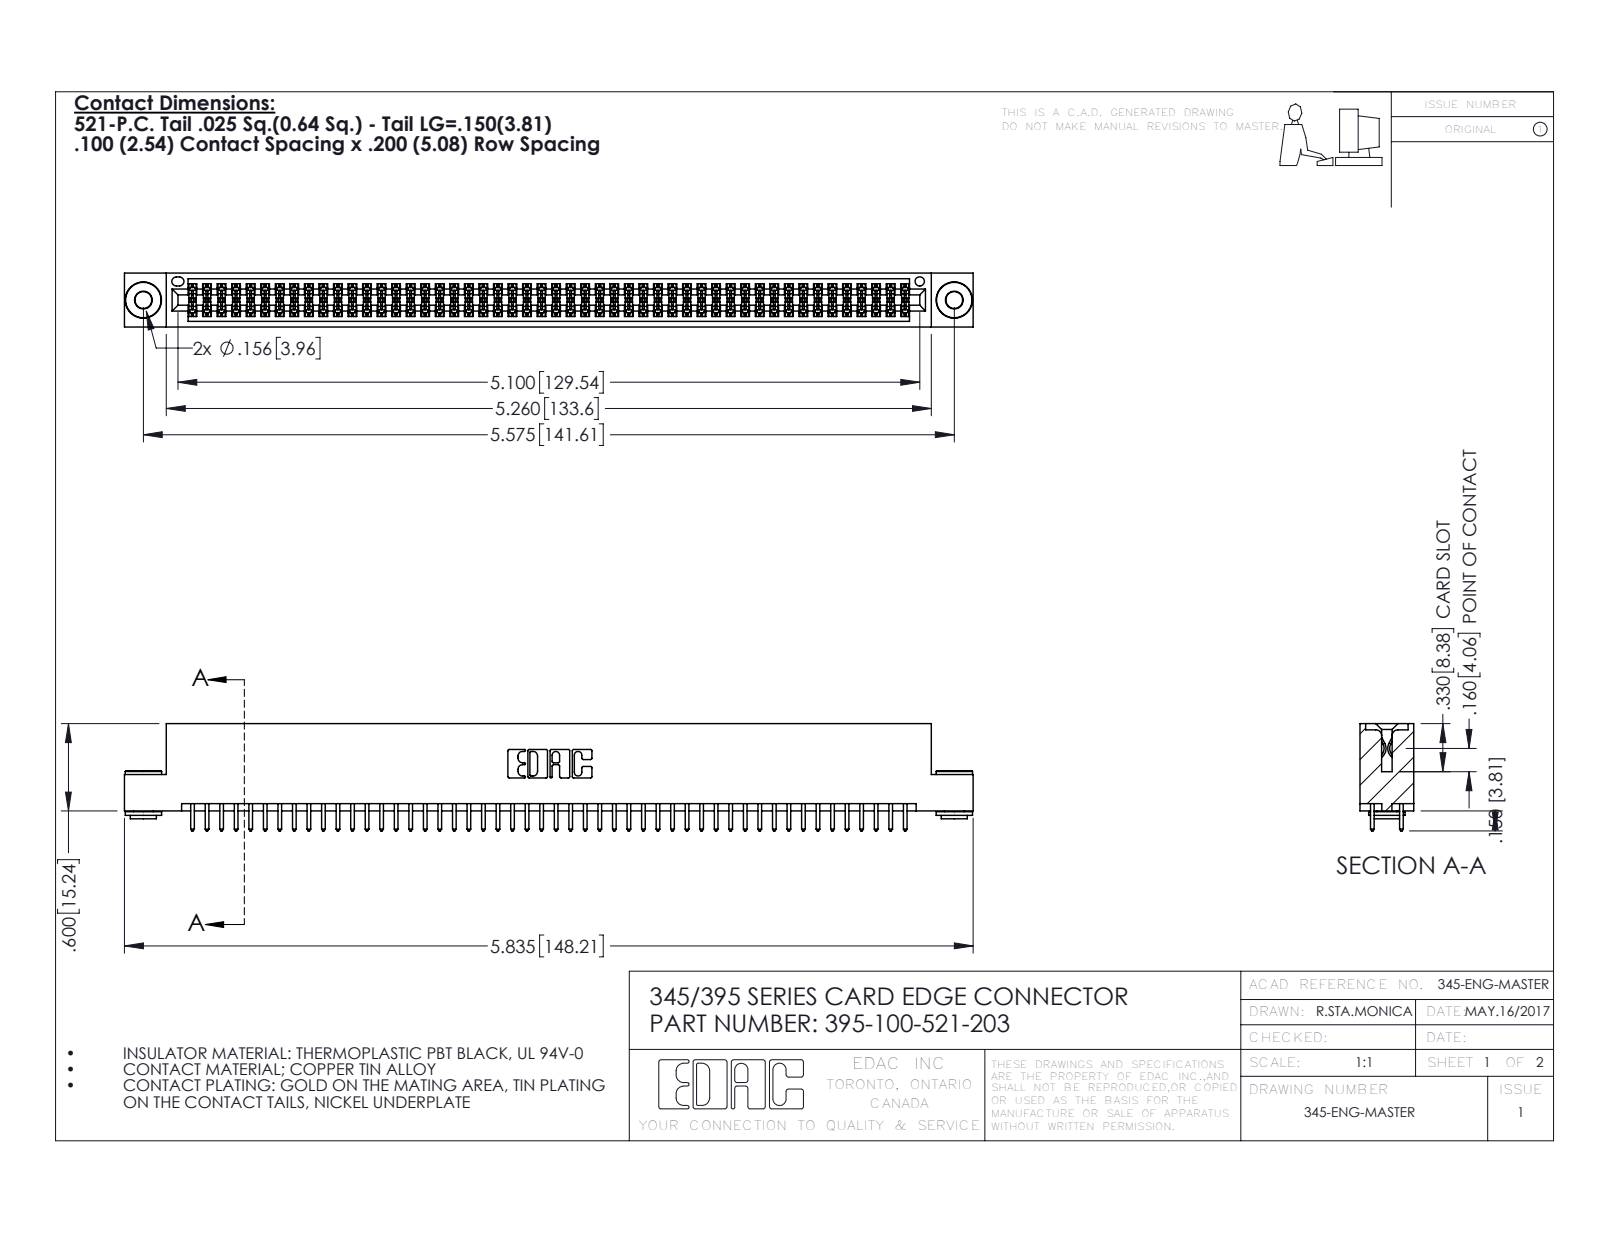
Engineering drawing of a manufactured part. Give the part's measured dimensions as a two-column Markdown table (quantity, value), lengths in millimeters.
| quantity | value |
| --- | --- |
| part name | 395-100-521-203; 345-292-001_345-293-121; 345 Part_Flush Mounting Lugs - 0.156 Dia-TH; 345-250-002_345-250-002-102 |
| STEP written by | SolidWorks 2016 (CONFIG_CONTROL_DESIGN) |
| units | millimeters |
| bodies | 103 solids, 5164 faces (3390 planar, 1766 cylindrical, 8 other) |
| overall size | 148.2 × 18.7 × 9.4 |
| volume | 14 500 mm³ |
| surface area | 21 450 mm² |
| round holes (diameter × count) | 2.9 × 2, 4 × 2, 1.6 × 1 |
| round bosses / shafts (diameter × count) | 6.4 × 2, 4.6 × 2, 3.5 × 2 |
| partial cylindrical surfaces (radius × count) | 0.2 × 150, 0.3 × 100, 0.3 × 22, 0.2 × 6, 0.8 × 6, 0.7 × 3, 0.4 × 2, 0.5 × 2 |
| main face-to-face distances | 1.8, 7.6, 5.1, 0.6, 9.4, 2.5, 6.9, 5.7, 4.4, 3.8 |
| hole center spacings | 6.9, 135.6, 141.6 |
